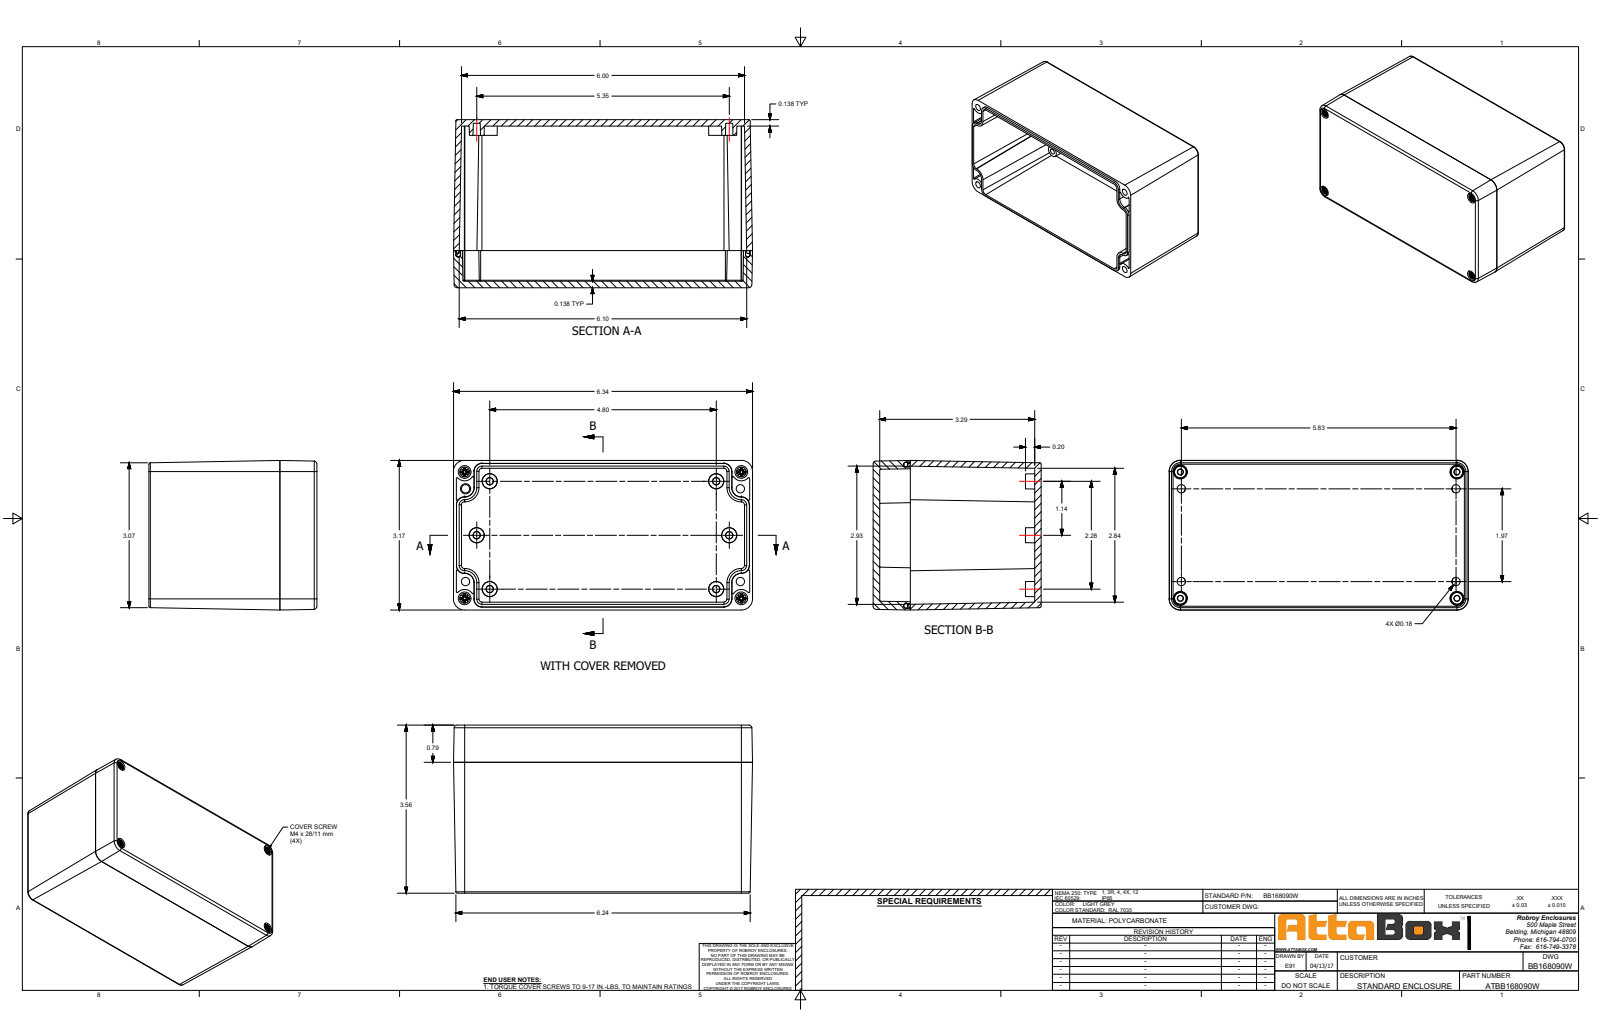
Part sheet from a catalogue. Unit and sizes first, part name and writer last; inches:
Units: inches
Overall size (bounding box): 6.339 × 3.564 × 3.169
Round holes (diameter × count): ⌀0.177 ×8, ⌀0.128 ×4, ⌀0.189 ×4, ⌀0.201 ×4, ⌀0.276 ×4, ⌀0.291 ×4, ⌀0.295 ×4
Round bosses / shafts (diameter × count): ⌀0.268 ×4, ⌀0.173 ×4, ⌀0.157 ×4, ⌀0.13 ×4
Partial cylindrical surfaces — rounded edges, fillets, slot ends (radius × count): R0.039 ×48, R0.02 ×38, R0.079 ×8, R0.177 ×8, R0.197 ×8, R0.031 ×4, R0.059 ×4, R0.102 ×4
Main face-to-face distances: 0.138, 3.425, 0.12, 3.563, 3.287, 3.049, 3.169, 0.122, 0.175, 2.874
Hole centre spacings: 0.355, 2.323, 5.857, 6.291, 1.969, 2.677, 5.827, 5.866
Volume: 14.18 in³ · Surface area: 252 in²
Bodies: 11 solids, 1640 faces (607 planar, 440 cylindrical, 593 other)
Part name (STEP PRODUCT): BB168090W
STEP written by: SolidWorks 2018 (AUTOMOTIVE_DESIGN)
